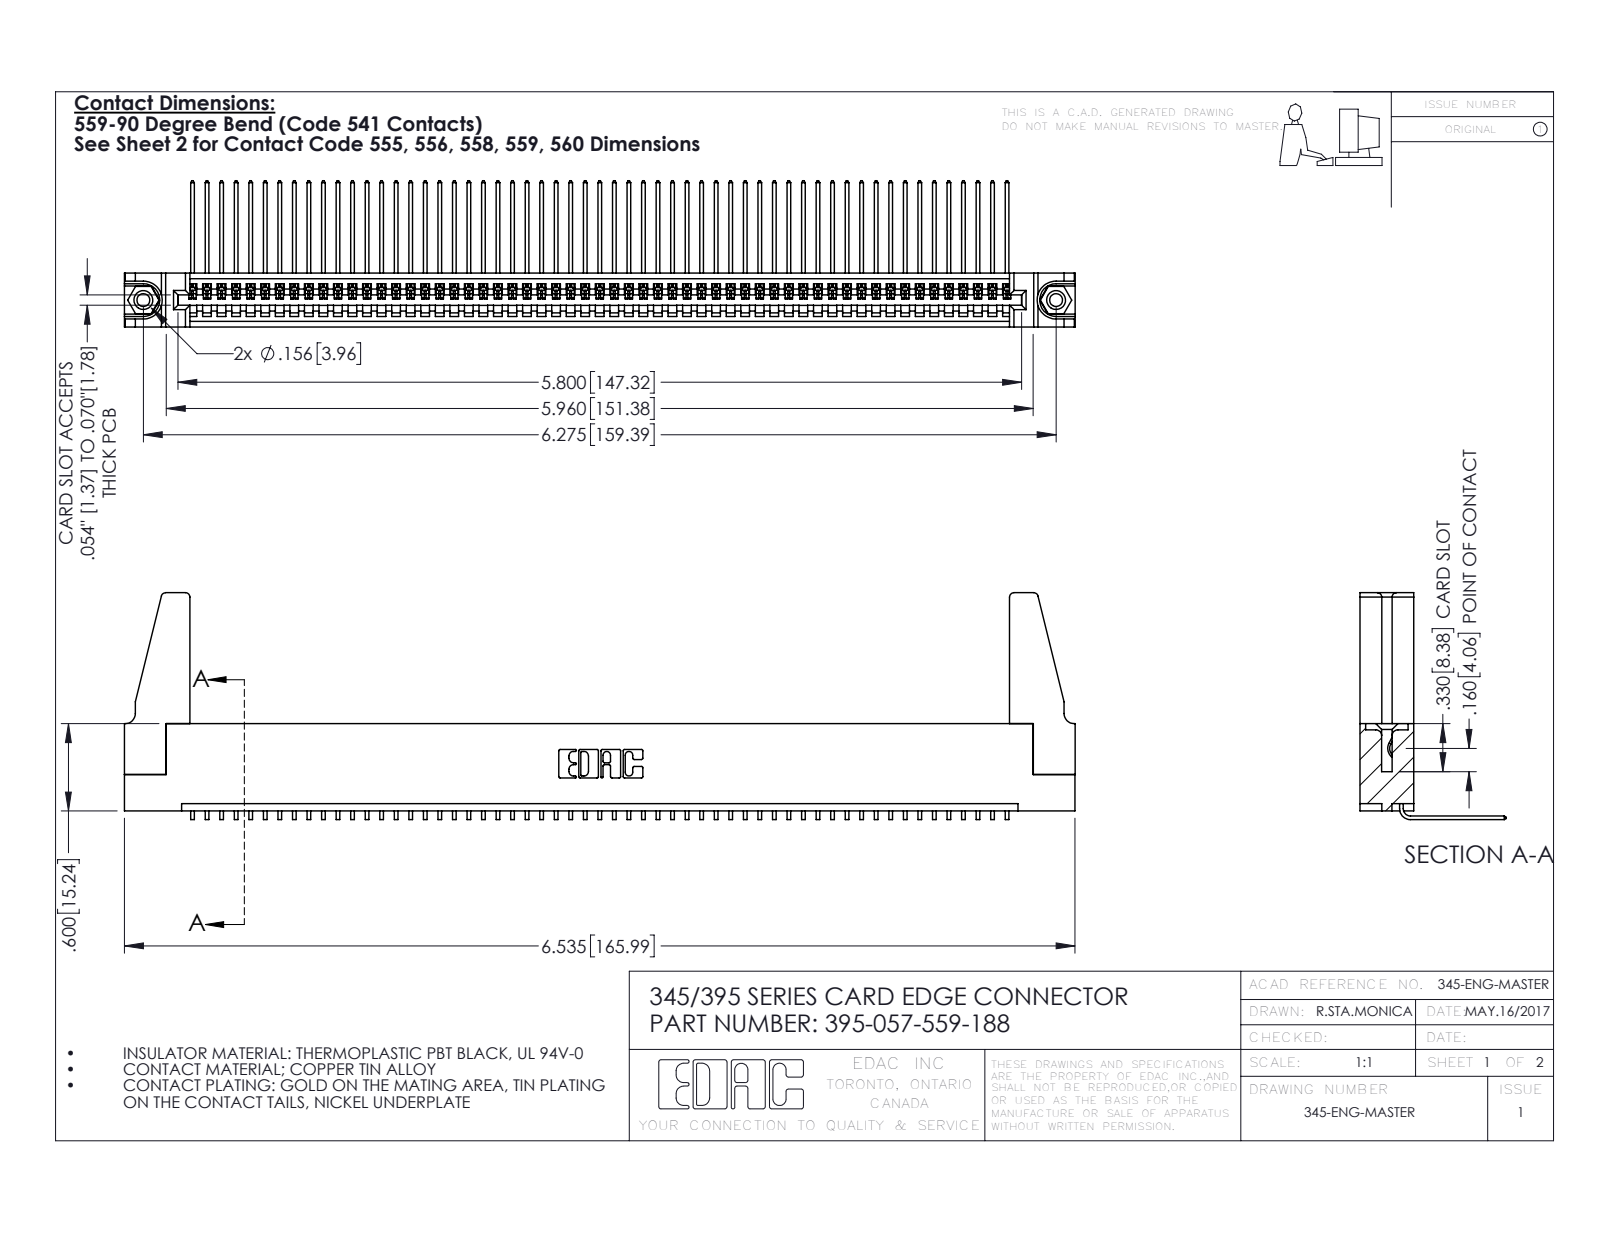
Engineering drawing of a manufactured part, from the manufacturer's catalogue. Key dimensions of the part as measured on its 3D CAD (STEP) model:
Part name (STEP PRODUCT): 345-292-001_558 559 Tail - 1; 345 Part_Flush Mounting Lugs - 0.156 Dia-TH; 395-057-559-188; 345-250-001_345-250-001-102 (+1 more)
STEP written by: SolidWorks 2016 (CONFIG_CONTROL_DESIGN)
Units: inches
Bodies: 62 solids, 3670 faces (2546 planar, 1108 cylindrical, 16 other)
Overall size (bounding box): 6.536 × 1.559 × 1.005
Volume: 1.18 in³ · Surface area: 40.02 in²
Round holes (diameter × count): ⌀0.089 ×2, ⌀0.125 ×2, ⌀0.156 ×2, ⌀0.064 ×1
Round bosses / shafts (diameter × count): ⌀0.155 ×2
Partial cylindrical surfaces — rounded edges, fillets, slot ends (radius × count): R0.006 ×114, R0.01 ×22, R0.03 ×8, R0.007 ×6, R0.031 ×6, R0.026 ×3, R0.031 ×2, R0.04 ×2
Main face-to-face distances: 0.072, 0.298, 0.37, 0.2, 0.098, 0.272, 0.025, 0.225, 0.149, 0.072
Hole centre spacings: 0.27, 6.039, 6.275
